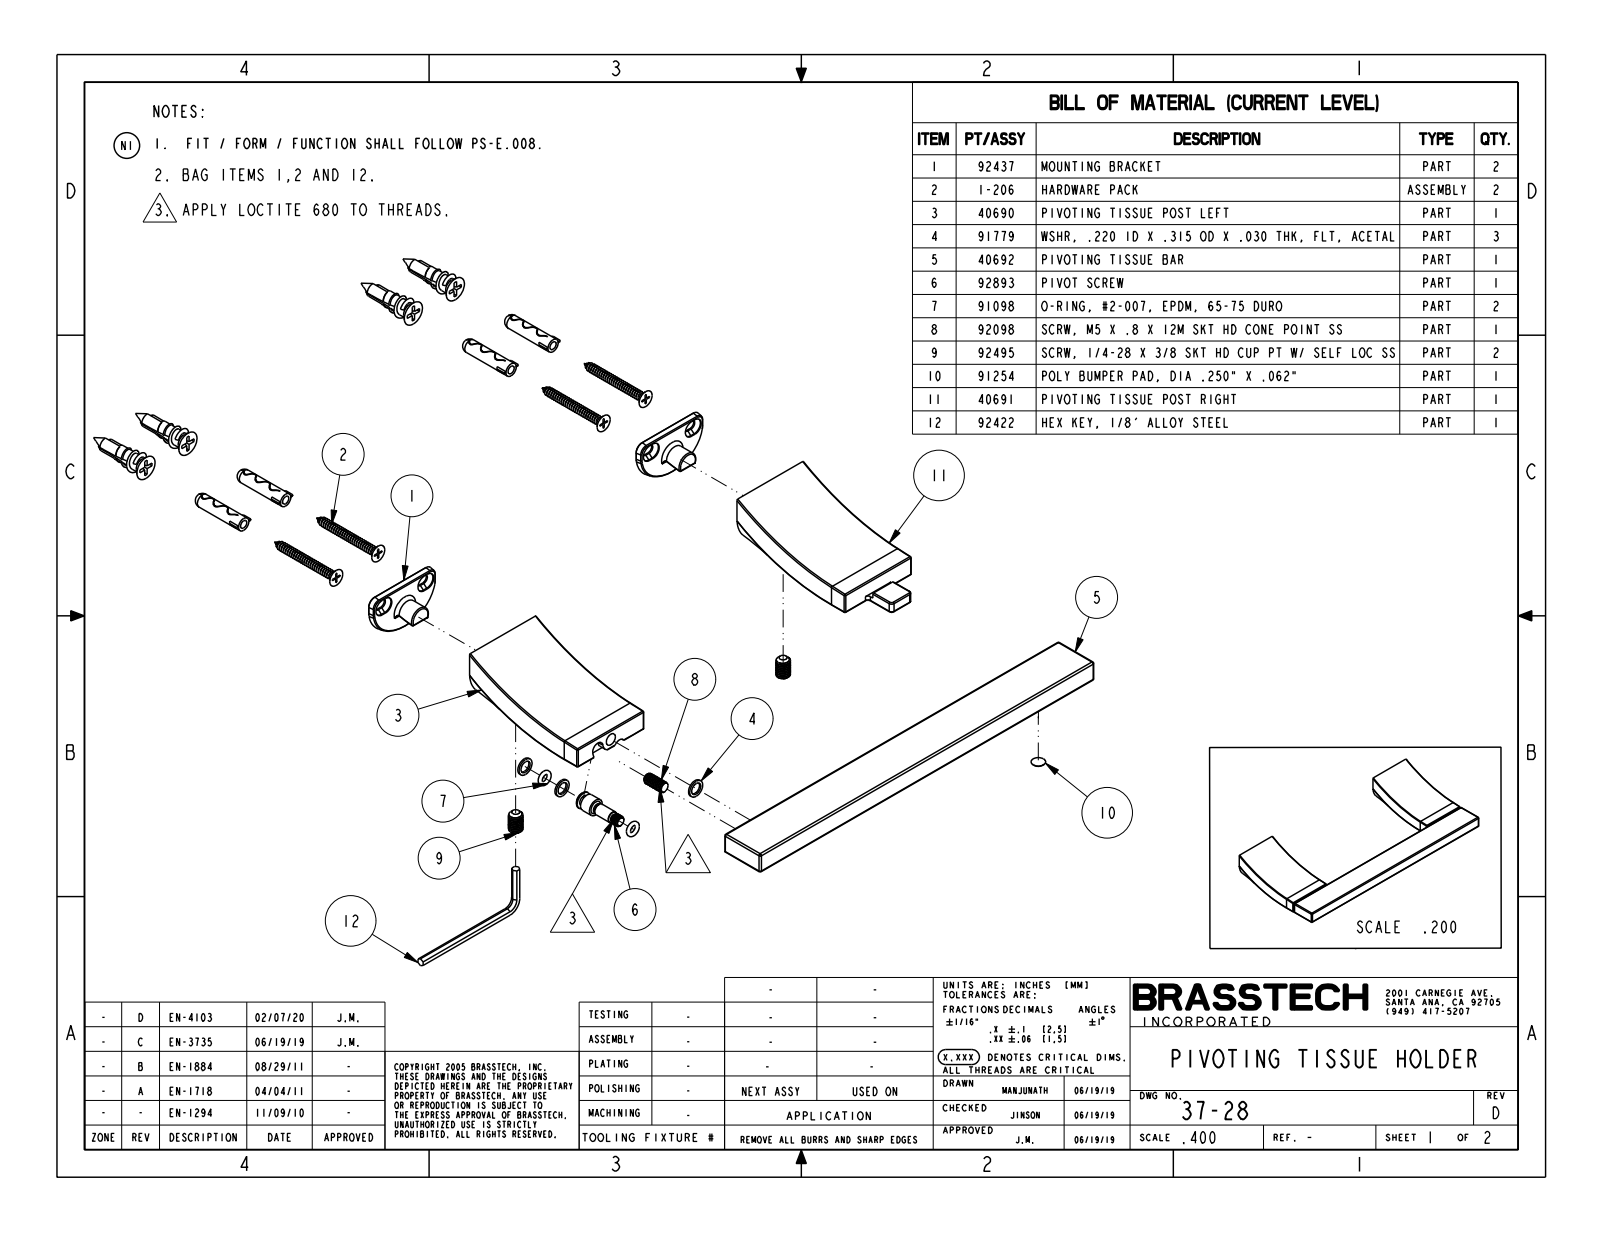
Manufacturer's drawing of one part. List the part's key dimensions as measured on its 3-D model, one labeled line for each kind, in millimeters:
Part name (STEP PRODUCT): 40437; 40430; 92441; 91100 (+8 more)
STEP written by: PRO/ENGINEER BY PARAMETRIC TECHNOLOGY CORPORATION, 2009300 (CONFIG_CONTROL_DESIGN)
Units: millimetres
Bodies: 15 solids, 877 faces (154 planar, 337 cylindrical, 386 other)
Overall size (bounding box): 206.4 × 89.9 × 27.4
Volume: 106 700 mm³ · Surface area: 60 210 mm²
Round holes (diameter × count): ⌀2.3 ×2, ⌀5.4 ×2, ⌀10.5 ×2, ⌀3 ×1, ⌀3.2 ×1, ⌀6.6 ×1, ⌀10.3 ×1
Round bosses / shafts (diameter × count): ⌀5.6 ×16, ⌀6.4 ×3, ⌀4.6 ×2, ⌀2.8 ×2, ⌀2 ×2, ⌀9.5 ×1
Partial cylindrical surfaces — rounded edges, fillets, slot ends (radius × count): R0.5 ×12, R0.8 ×12, R2.3 ×8, R3.9 ×8, R1.5 ×4, R1.6 ×4, R2.8 ×4, R3.2 ×2
Main face-to-face distances: 8.9, 86.9, 64.7, 22.2, 67.7, 3, 89.9, 0.6, 67.1, 64.1
Hole centre spacings: 165.1, 6.4, 8.1, 11.1, 66.5, 165.2, 173.3, 178.1
